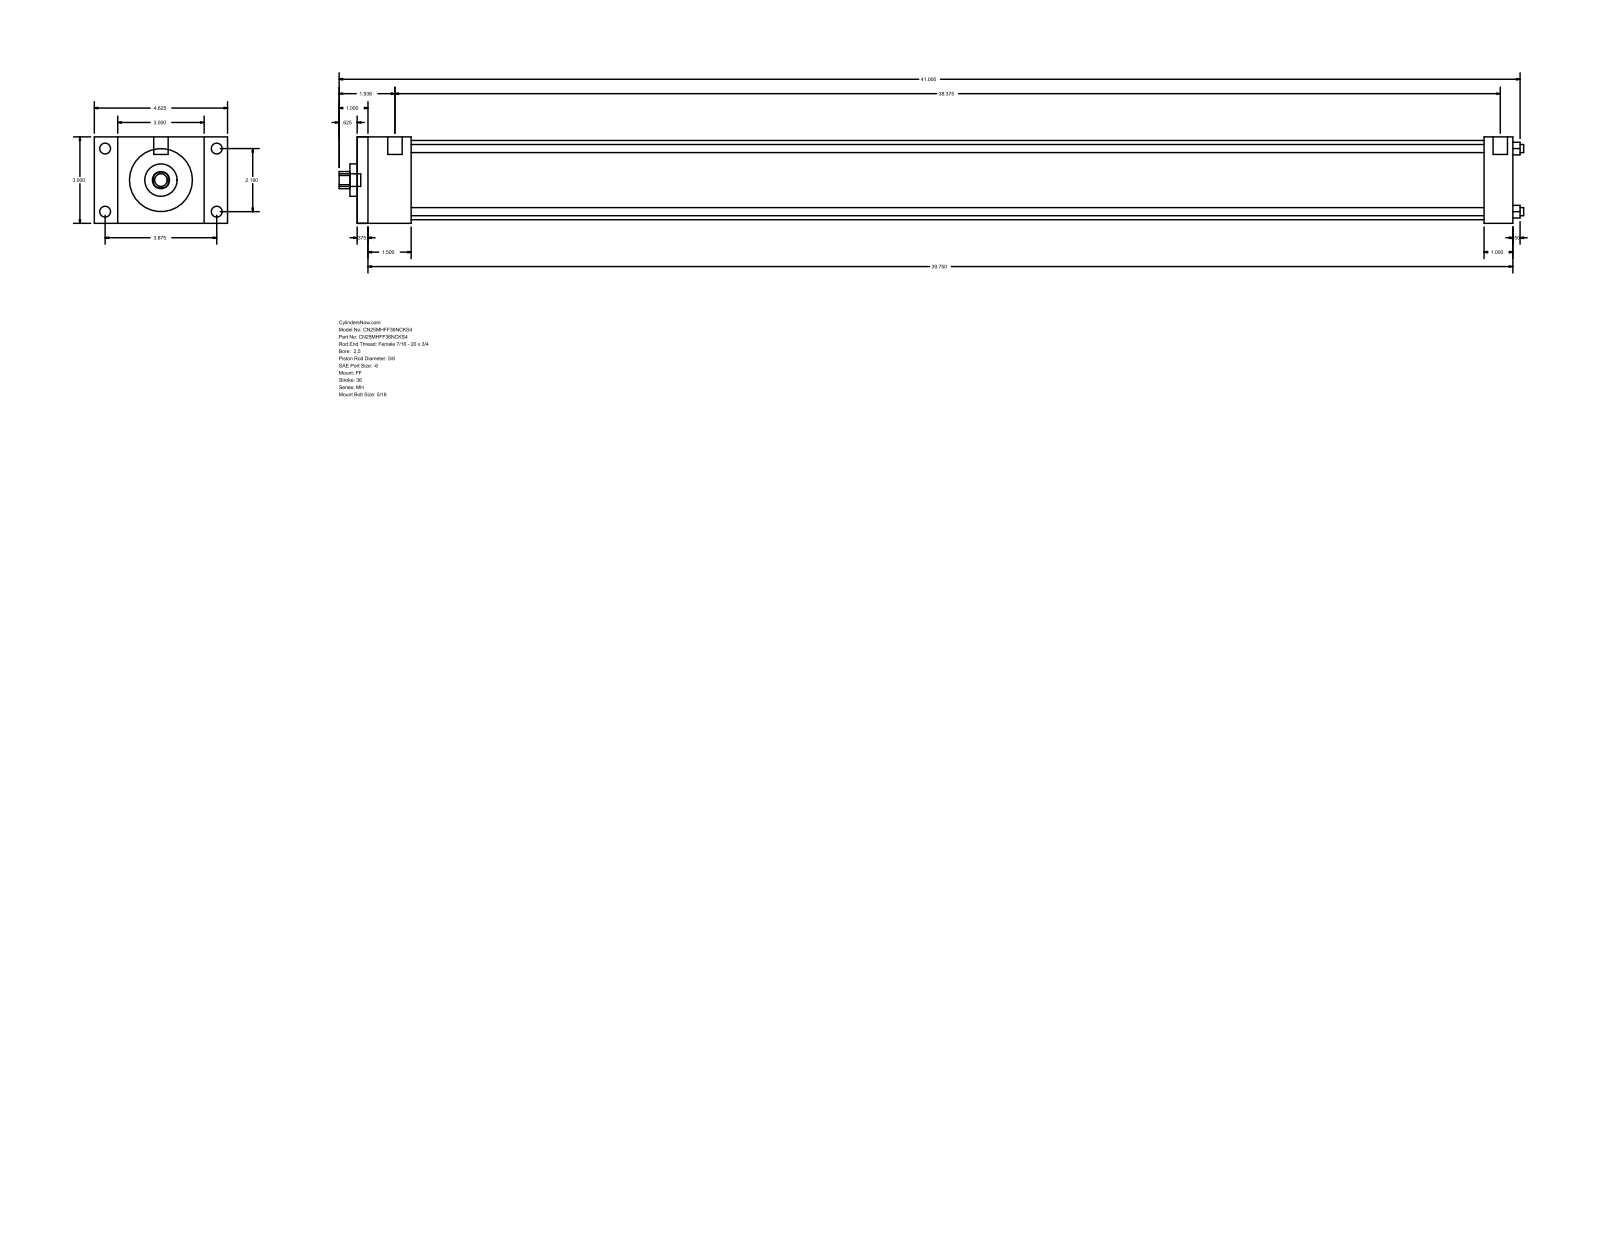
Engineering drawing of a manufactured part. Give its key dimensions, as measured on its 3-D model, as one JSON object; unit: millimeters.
{"part_name": "MH_FF__0250_0.625", "step_written_by": "GSSL Pune (CONFIG_CONTROL_DESIGN)", "units": "millimeters", "bodies": {"solids": 0, "faces": 92, "planar": 64, "cylindrical": 28, "other": 0}, "overall_size": [1044.58, 117.47, 76.2], "round_holes": [[7.14, 4], [15.88, 1], [28.57, 1], [69.85, 1]], "round_bosses_or_shafts": [[9.53, 4], [5.56, 4], [12.7, 2], [11.11, 1]], "partial_cylinders_radius": [[7.54, 1]], "face_to_face_distances": [76.2, 1019.17, 9.52, 1009.65, 25.4, 47.62, 993.77, 38.1, 984.25, 946.15], "hole_center_spacings": [39.33, 55.62, 78.66]}
